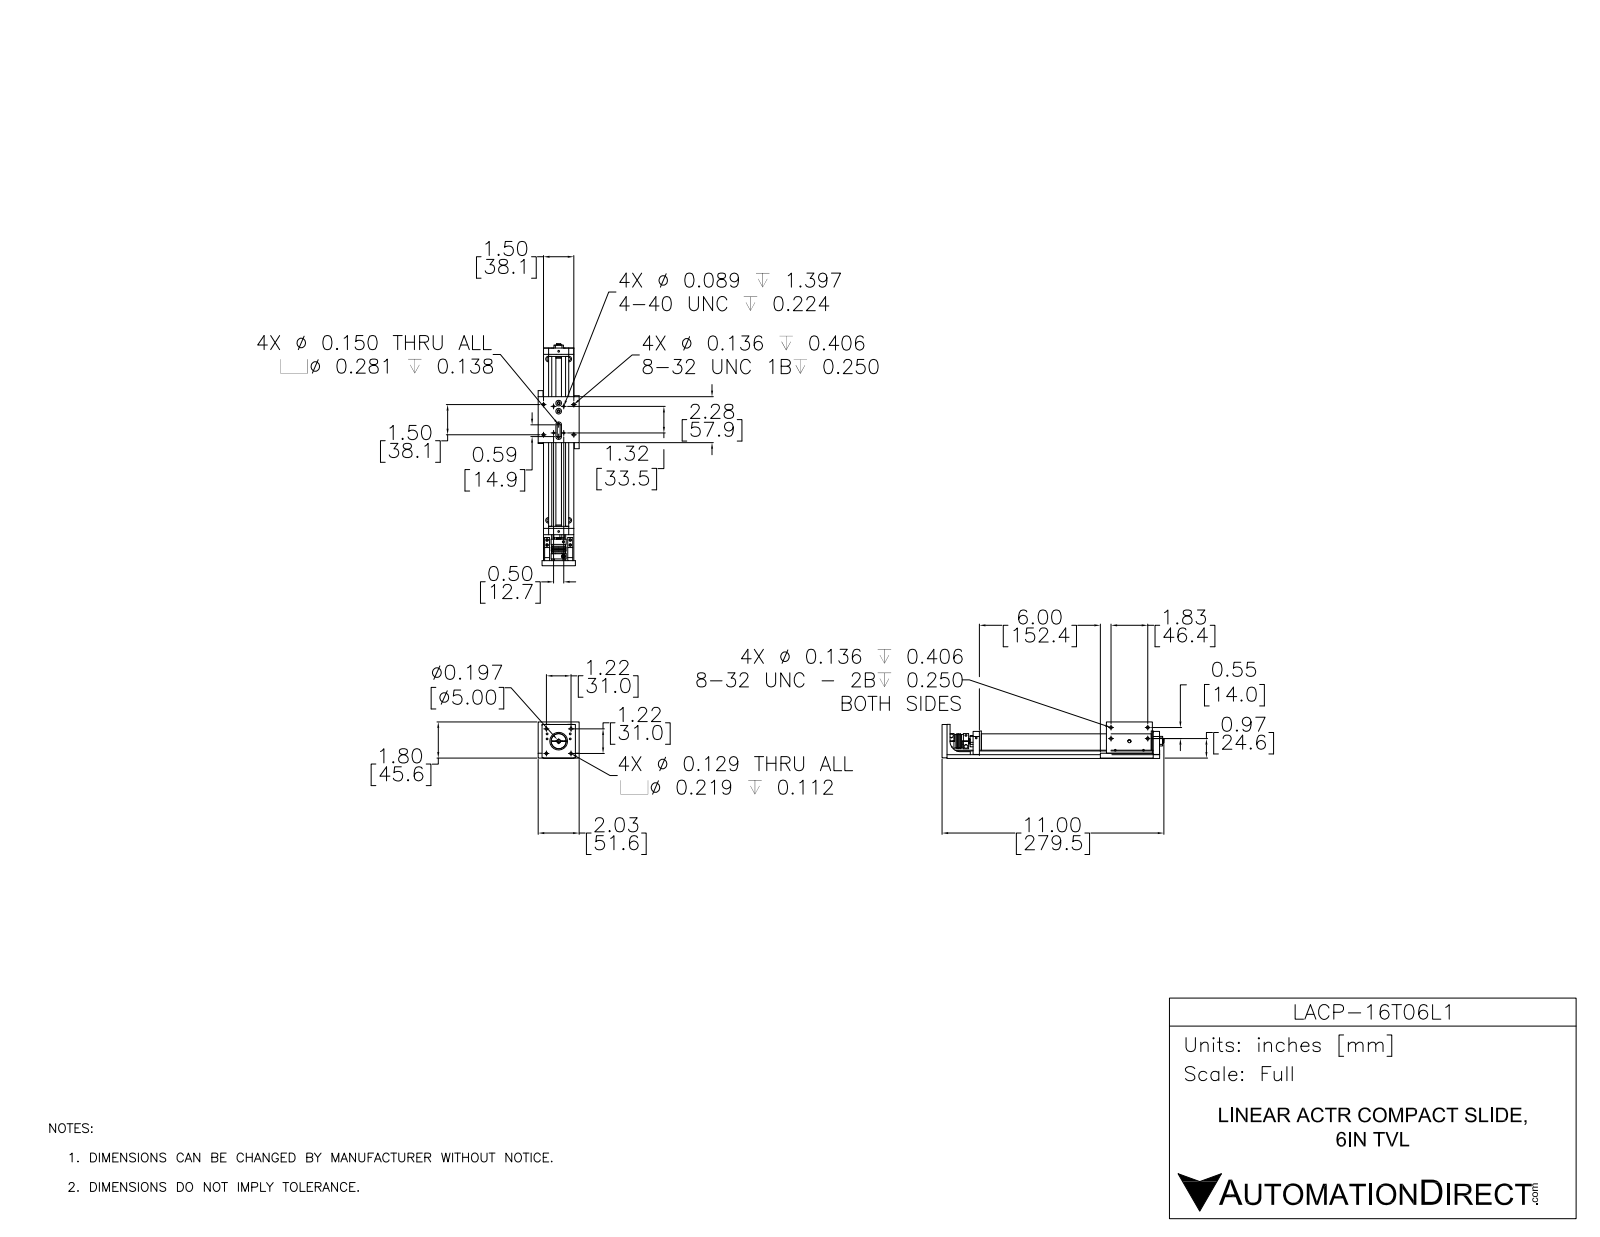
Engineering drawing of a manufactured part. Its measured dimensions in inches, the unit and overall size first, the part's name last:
Units: inches
Overall size (bounding box): 10.995 × 2.03 × 1.812
Round holes (diameter × count): ⌀0.089 ×16, ⌀0.136 ×8, ⌀0.281 ×8, ⌀0.17 ×6, ⌀0.15 ×5, ⌀0.07 ×4, ⌀0.129 ×4, ⌀0.129 ×4, ⌀0.219 ×4, ⌀0.138 ×3, ⌀0.197 ×3, ⌀0.081 ×2
Round bosses / shafts (diameter × count): ⌀0.157 ×3, ⌀0.15 ×2, ⌀1 ×1, ⌀0.748 ×1, ⌀0.71 ×1, ⌀0.673 ×1, ⌀0.67 ×1, ⌀0.59 ×1
Partial cylindrical surfaces — rounded edges, fillets, slot ends (radius × count): R0.047 ×4, R0.062 ×4, R0.094 ×4, R0.125 ×3, R0.05 ×2, R0.075 ×2, R0.141 ×2, R0.25 ×2
Main face-to-face distances: 0.187, 0.265, 0.25, 1.765, 1.624, 1.812, 2.03, 1.465, 0.256, 0.068
Hole centre spacings: 0.5, 4.031, 4, 0.25, 0.418, 0.508, 0.863, 1.004
Volume: 15.62 in³ · Surface area: 183.8 in²
Bodies: 25 solids, 805 faces (269 planar, 454 cylindrical, 82 other)
Part name (STEP PRODUCT): LACP-16TXXL1-CAR; LACP-16T06L1-RAIL; LACP-16T06L1
STEP written by: SolidWorks 2016 (AUTOMOTIVE_DESIGN)
